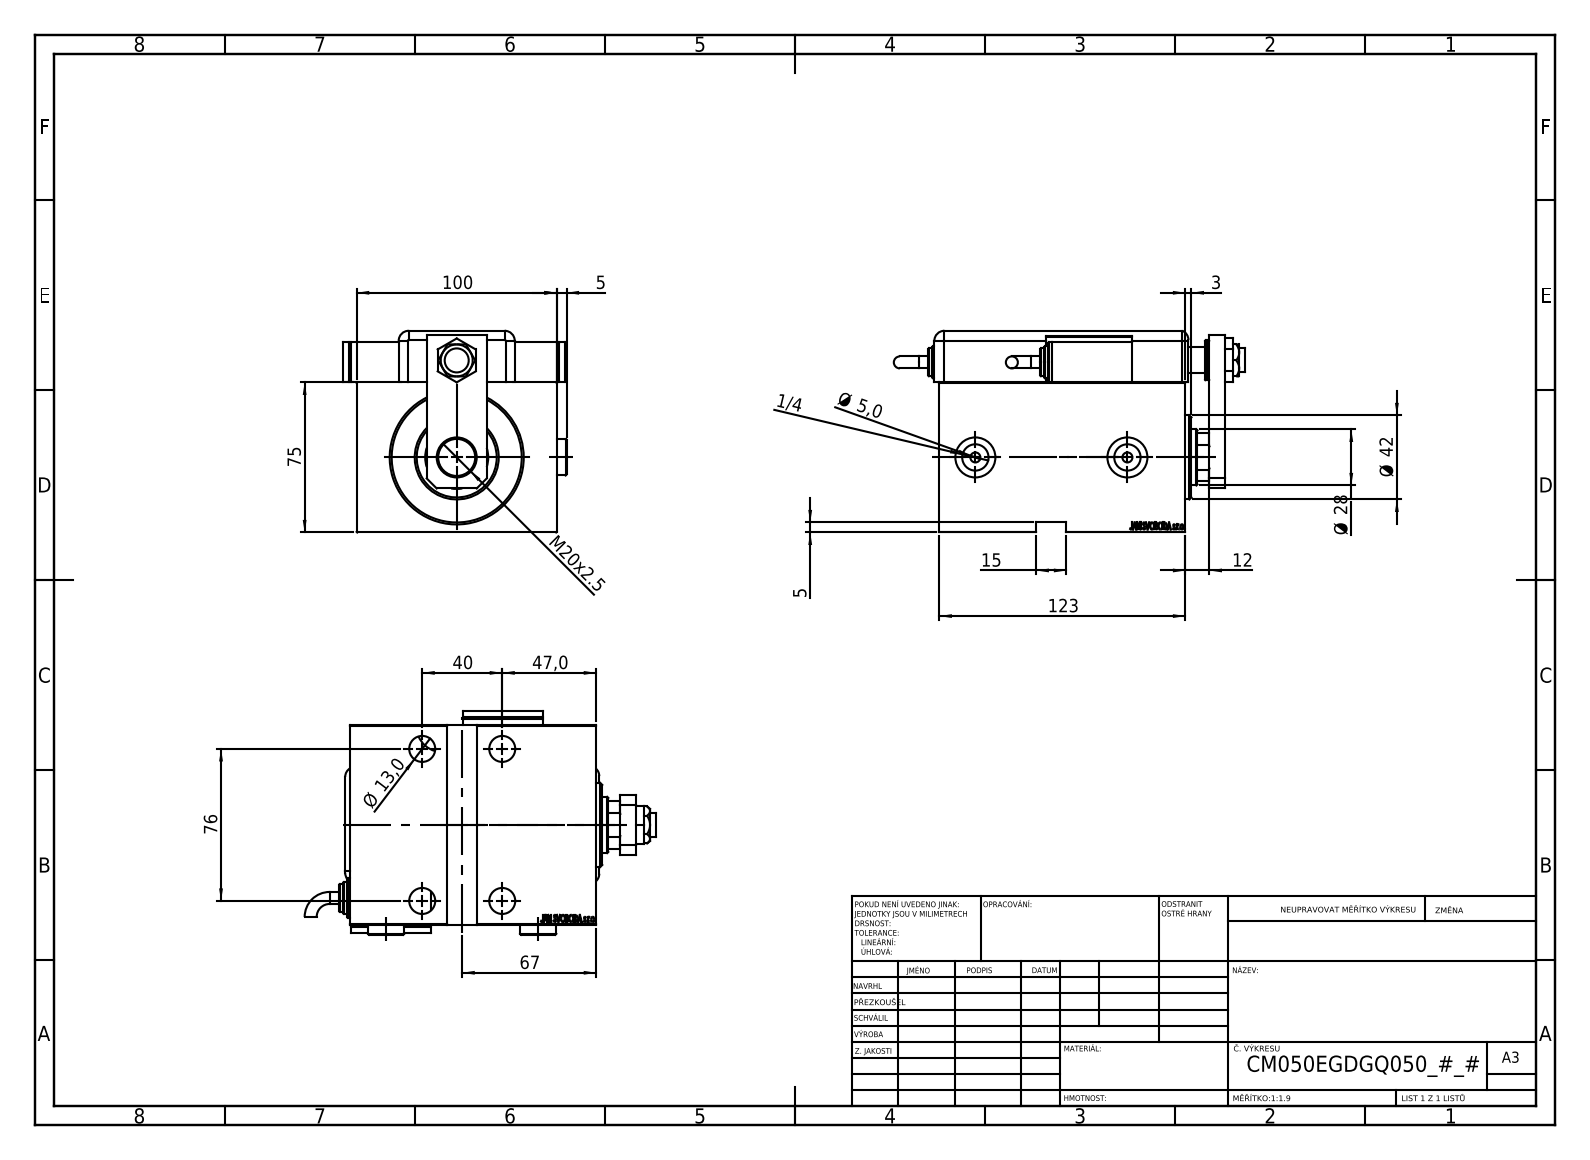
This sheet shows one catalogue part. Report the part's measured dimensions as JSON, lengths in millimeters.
{"part_name": "MAGNETIC SWITCH Q; NUT_D19; SWITCH Q; Zatka_OIL_PORT (+7 more)", "step_written_by": "SolidWorks 2019 (CONFIG_CONTROL_DESIGN)", "units": "millimeters", "bodies": {"solids": 15, "faces": 1296, "planar": 652, "cylindrical": 123, "other": 521}, "overall_size": [175.46, 111.9, 100.8], "volume_mm3": 951622, "surface_area_mm2": 183517, "round_holes": [[13, 5], [19, 4], [20, 3], [4, 2], [5, 2], [8, 2], [13.16, 2], [12, 1], [14, 1], [18.5, 1], [28, 1], [31.5, 1]], "round_bosses_or_shafts": [[20, 3], [18, 2], [16, 2], [14, 2], [6, 2], [52, 1], [42, 1]], "partial_cylinders_radius": [[5, 9], [10, 1], [13.5, 1]], "face_to_face_distances": [3, 75, 100, 123, 100.8, 25.8, 14, 20, 109, 5], "hole_center_spacings": [76, 40, 47.2, 61.22, 82.87, 85.88, 91.59, 20]}
